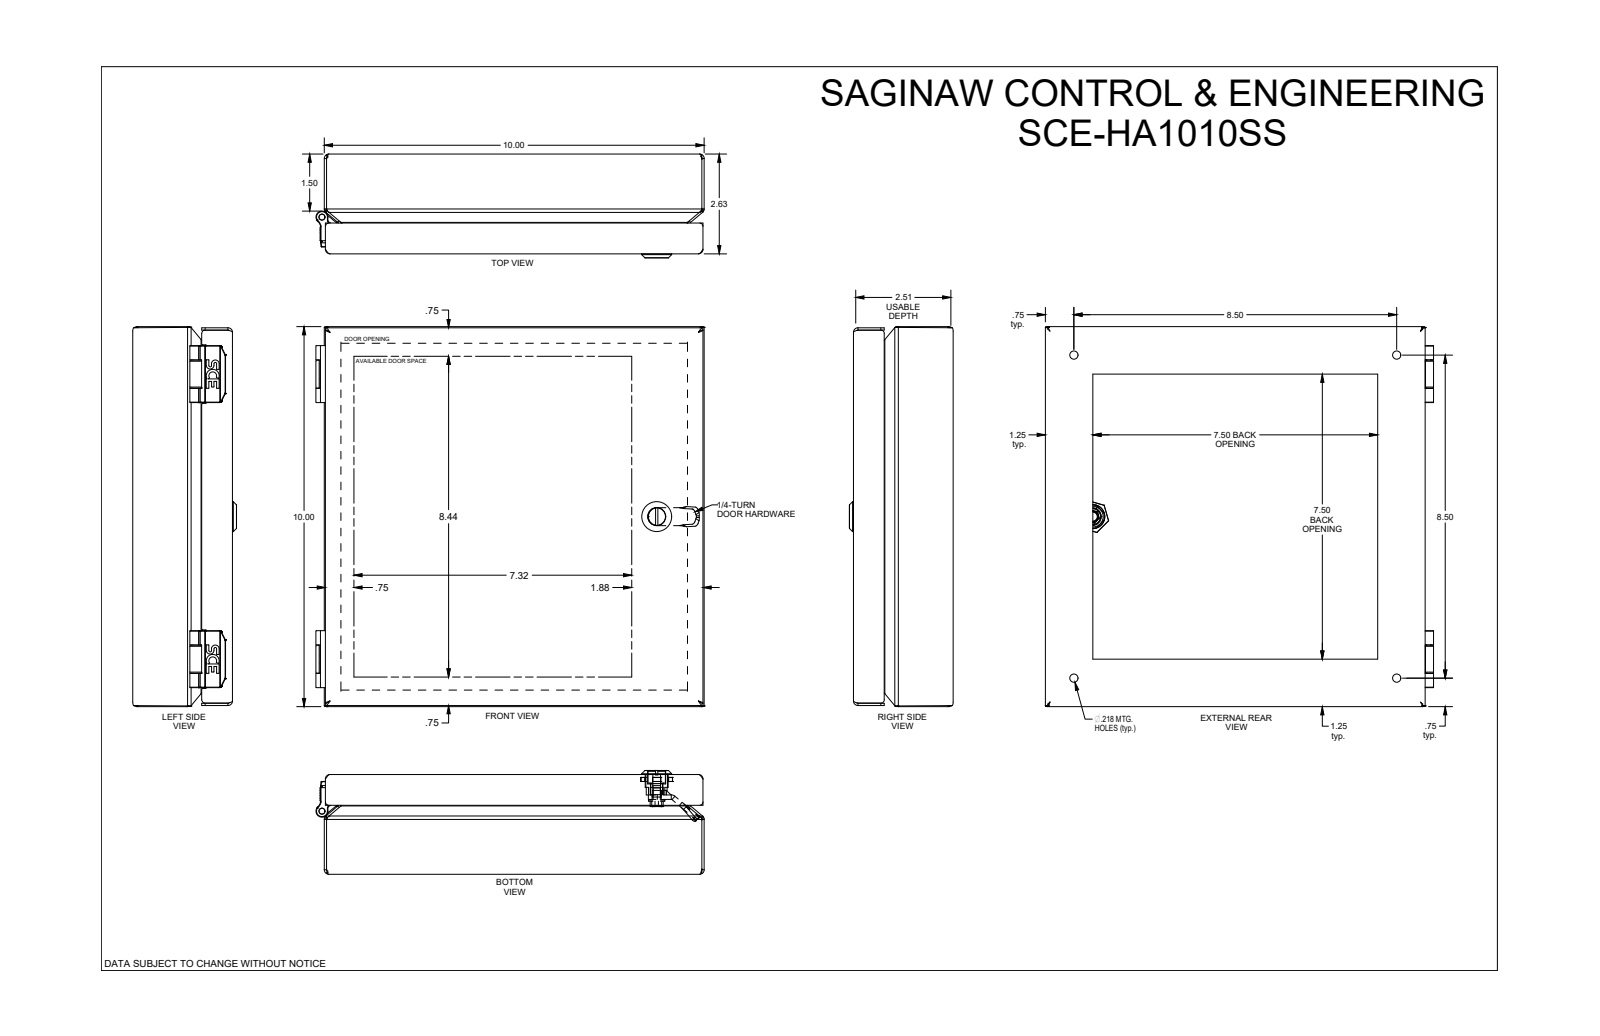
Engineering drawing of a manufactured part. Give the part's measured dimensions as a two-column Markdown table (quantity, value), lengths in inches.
| quantity | value |
| --- | --- |
| part name | SCE-HA1010 |
| STEP written by | SolidWorks 2021 (AUTOMOTIVE_DESIGN) |
| units | inches |
| bodies | 16 solids, 1069 faces (312 planar, 347 cylindrical, 410 other) |
| overall size | 10.22 × 10.06 × 2.732 |
| volume | 16.63 in³ |
| surface area | 558.6 in² |
| round holes (diameter × count) | 0.218 × 4, 0.17 × 2, 0.158 × 1, 0.196 × 1, 0.2 × 1, 0.239 × 1, 0.254 × 1, 0.269 × 1, 0.282 × 1, 0.326 × 1, 0.475 × 1, 0.63 × 1 |
| round bosses / shafts (diameter × count) | 0.479 × 2, 0.26 × 2, 0.1 × 2, 0.02 × 2, 0.788 × 1, 0.548 × 1, 0.46 × 1, 0.43 × 1 |
| partial cylindrical surfaces (radius × count) | 0.106 × 66, 0.005 × 36, 0.008 × 32, 0.013 × 21, 0.05 × 16, 0.025 × 12, 0.01 × 10, 0.06 × 10 |
| main face-to-face distances | 0.059, 0.06, 10.001, 2.565, 2.625, 2.506, 2.566, 10.06, 9.942, 9.97 |
| hole center spacings | 8.552, 12.094, 1.178, 4.275, 4.334, 7.411, 7.5, 8.36 |
